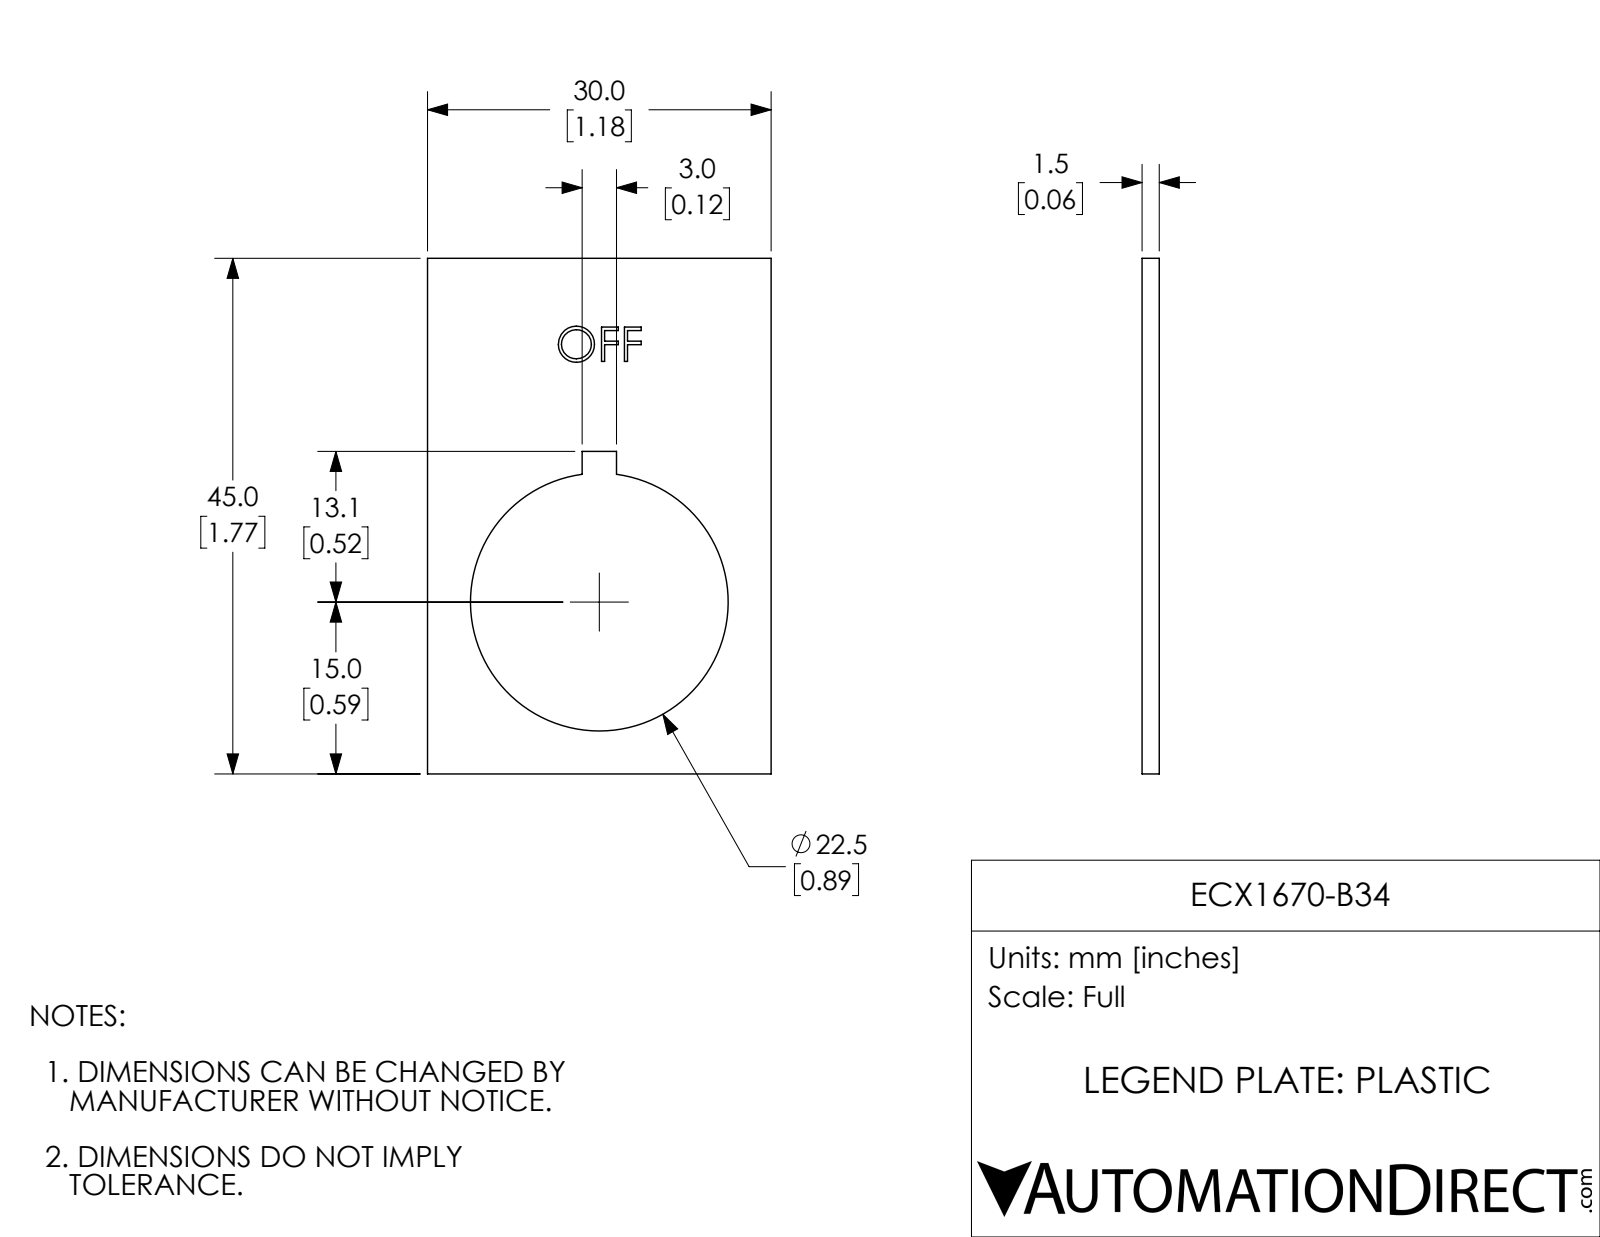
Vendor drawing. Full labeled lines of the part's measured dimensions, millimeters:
Part name (STEP PRODUCT): ECX1670-B34
STEP written by: SolidWorks 2017 (AUTOMOTIVE_DESIGN)
Units: millimetres
Bodies: 1 solid, 44 faces (33 planar, 3 cylindrical, 8 other)
Overall size (bounding box): 45 × 30 × 1.5
Volume: 1 400 mm³ · Surface area: 2 231 mm²
Round holes (diameter × count): ⌀22.5 ×1
Main face-to-face distances: 1.5, 30, 45, 13.5, 16.5, 1.5, 28.1, 16.8, 3, 2
